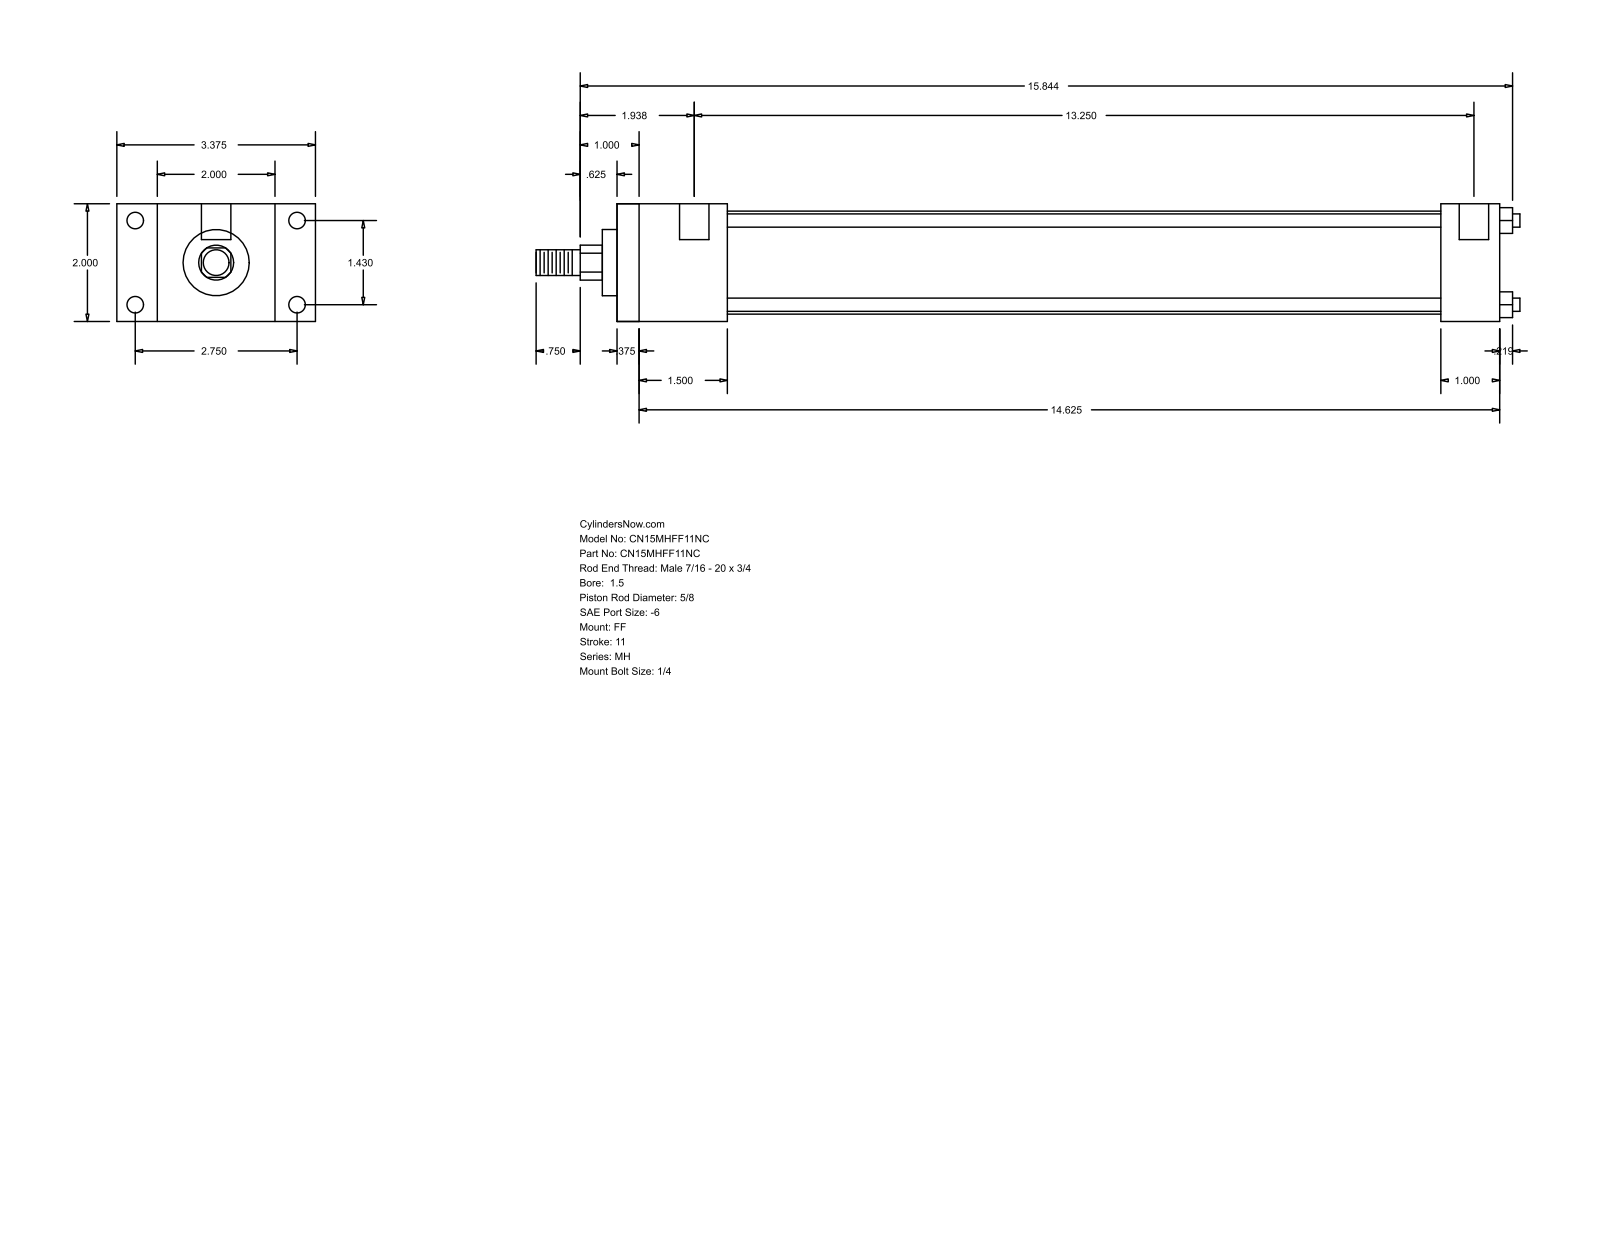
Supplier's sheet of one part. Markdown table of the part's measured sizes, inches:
| quantity | value |
| --- | --- |
| part name | MH_FF__0150_0.625 |
| STEP written by | GSSL Pune (CONFIG_CONTROL_DESIGN) |
| units | inches |
| bodies | 0 solids, 92 faces (64 planar, 28 cylindrical, 0 other) |
| overall size | 16.719 × 3.375 × 2 |
| round holes (diameter × count) | 0.219 × 4, 0.281 × 4, 0.5 × 2 |
| round bosses / shafts (diameter × count) | 0.225 × 4, 1.75 × 1, 1.125 × 1, 0.625 × 1, 0.437 × 1 |
| partial cylindrical surfaces (radius × count) | 0.297 × 1 |
| main face-to-face distances | 2, 15, 14.625, 0.375, 1, 0.687, 2.687, 1.875, 1.5, 13.125 |
| hole center spacings | 1.43, 2.75, 3.099, 13.375, 0.125, 13.25 |
